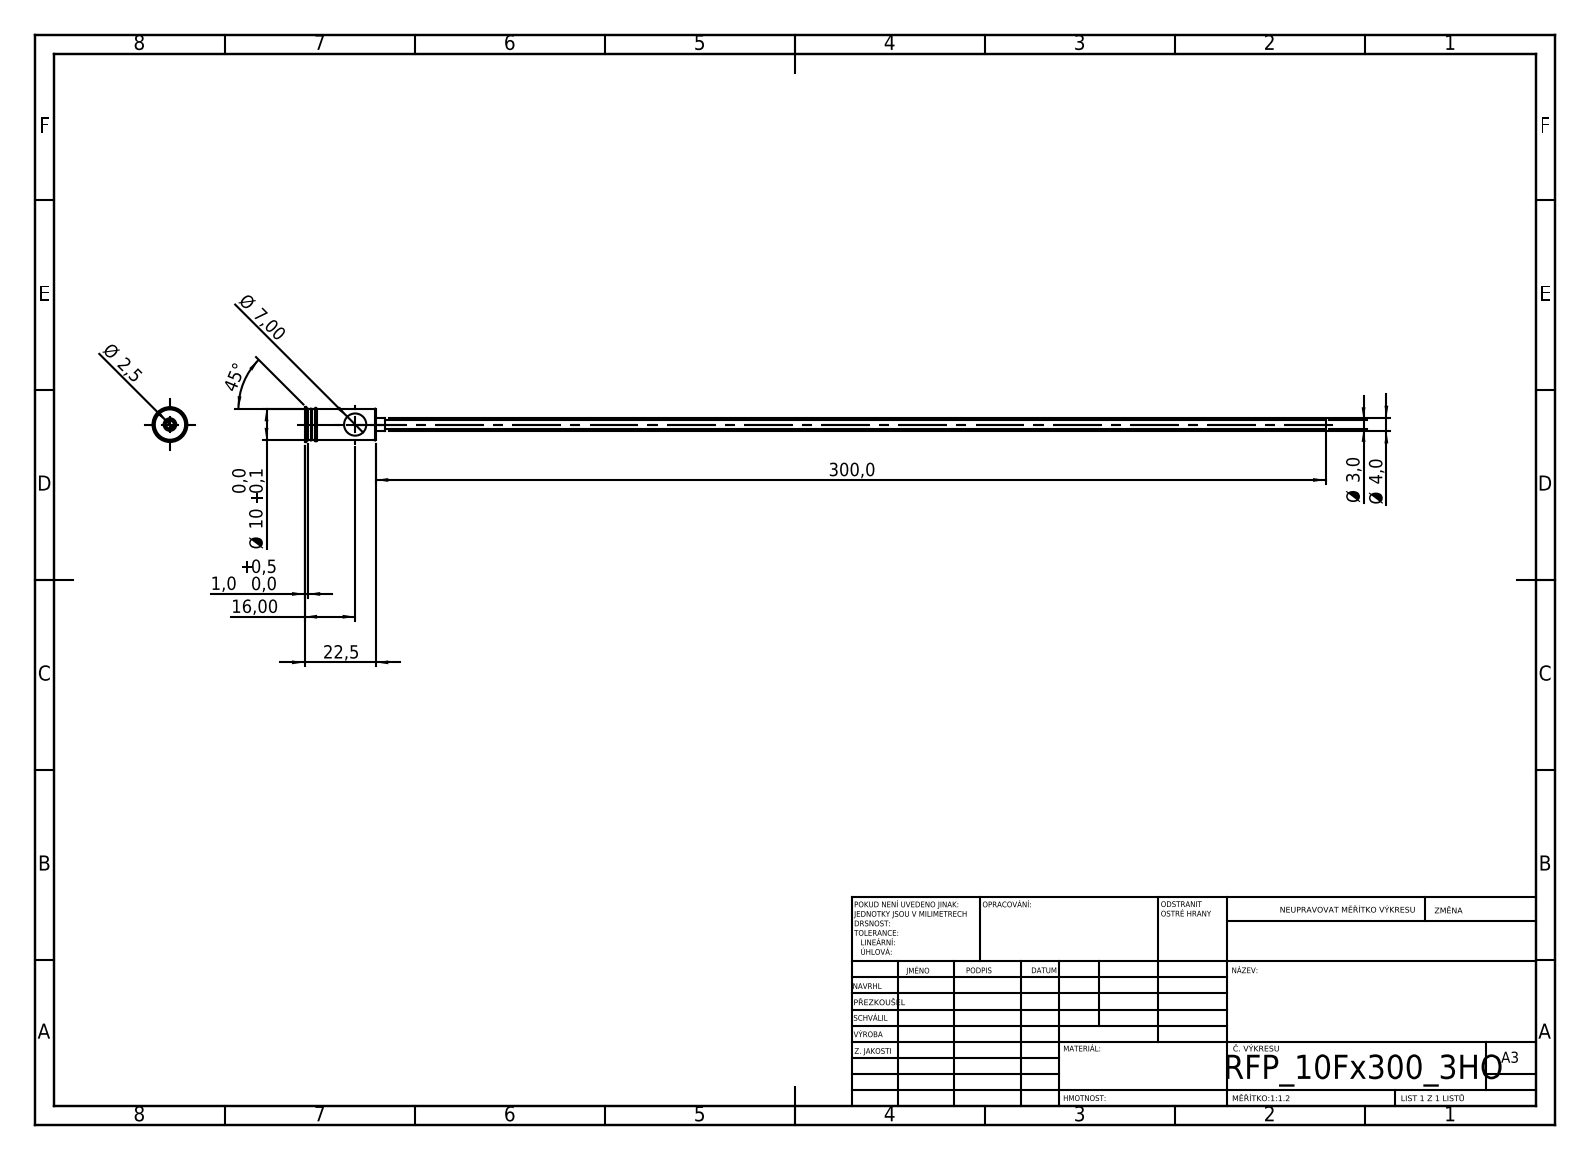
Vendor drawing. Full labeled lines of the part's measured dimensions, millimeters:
STEP written by: SolidWorks 2019 (CONFIG_CONTROL_DESIGN)
Units: millimetres
Bodies: 1 solid, 44 faces (20 planar, 16 cylindrical, 8 other)
Overall size (bounding box): 322.5 × 11 × 11
Volume: 2 020 mm³ · Surface area: 6 261 mm²
Round holes (diameter × count): ⌀2.5 ×1, ⌀7 ×1
Round bosses / shafts (diameter × count): ⌀11 ×1, ⌀10 ×1, ⌀4 ×1, ⌀3 ×1
Main face-to-face distances: 22.5, 20.5, 2, 5.4, 20.2, 2.3, 3, 23.2, 23.5, 25.5
